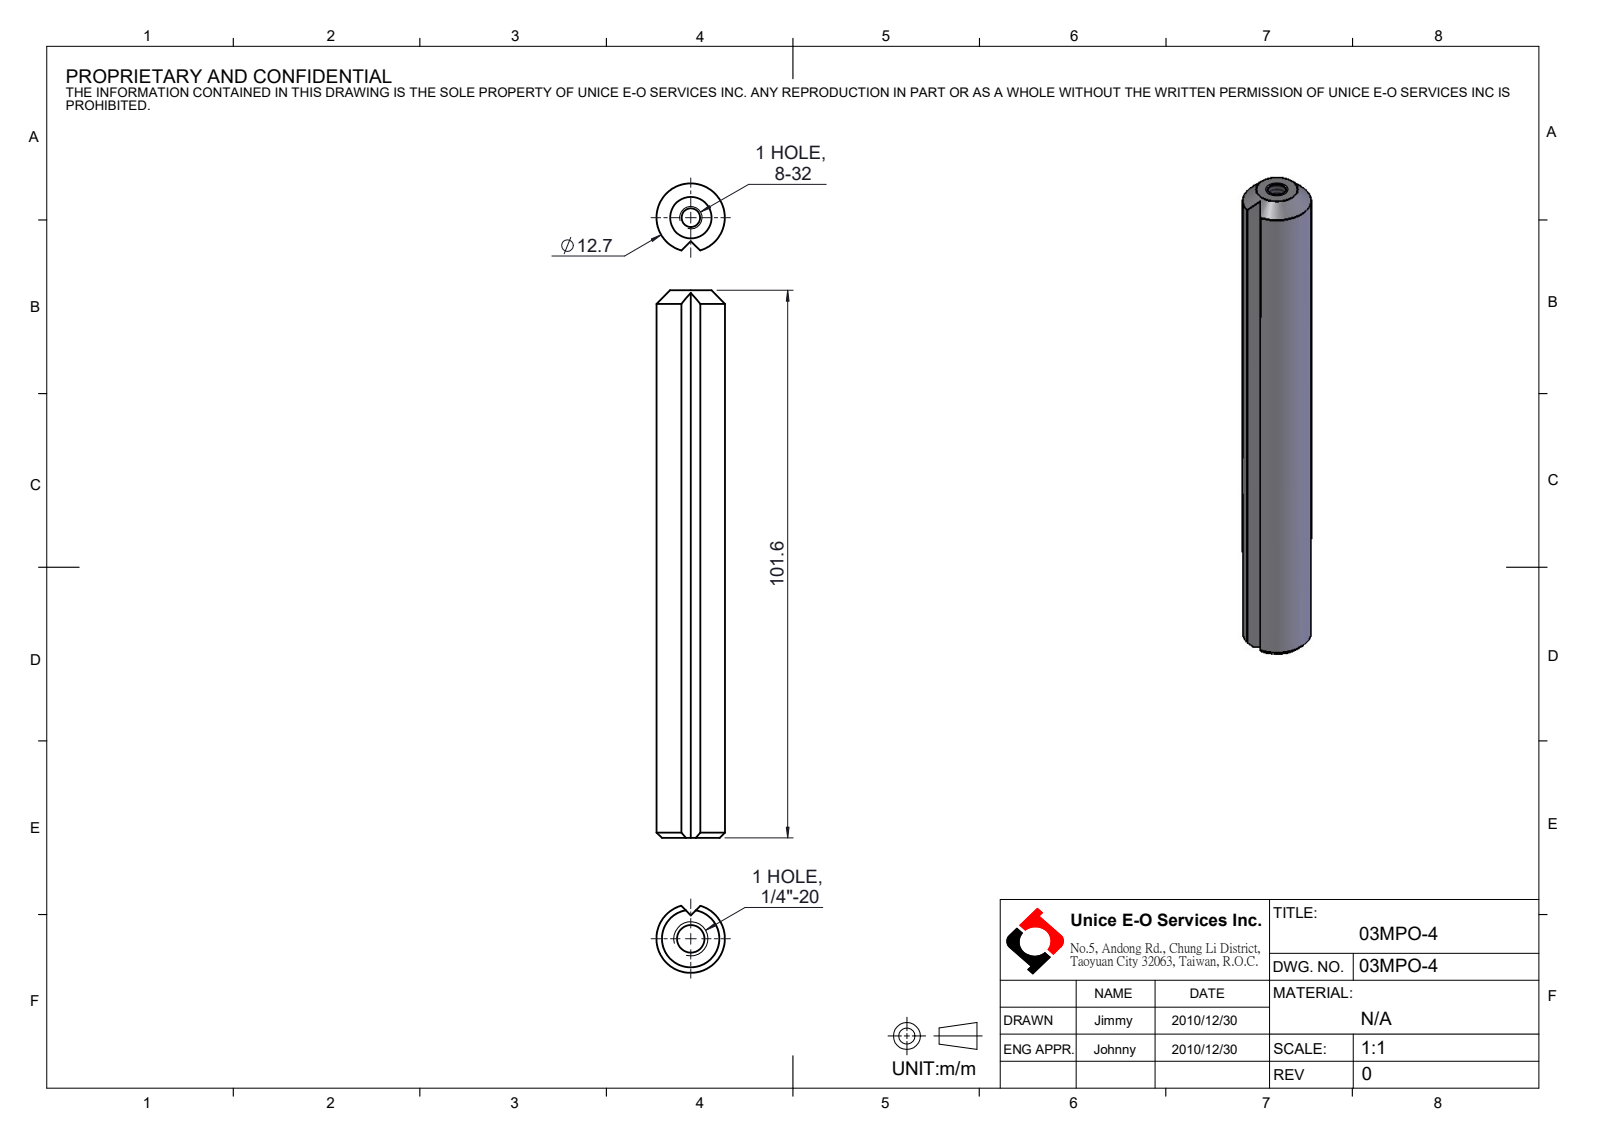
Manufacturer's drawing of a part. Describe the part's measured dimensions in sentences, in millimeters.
The part is named "03MPO-4". Its 3-D file was written by "SolidWorks 2016 (CONFIG_CONTROL_DESIGN)". It is 1 solid with 17 faces: 4 planar, 6 cylindrical and 7 other. Overall it measures 101.6 by 12.7 by 12.45 millimeters. Its volume is 11 967 cubic millimeters and its surface area 4 707 square millimeters. Round holes: 1 of diameter 3.45, 1 of diameter 5.11. Round bosses or shafts: 1 of diameter 12.7. The main face-to-face distances are 101.6.
